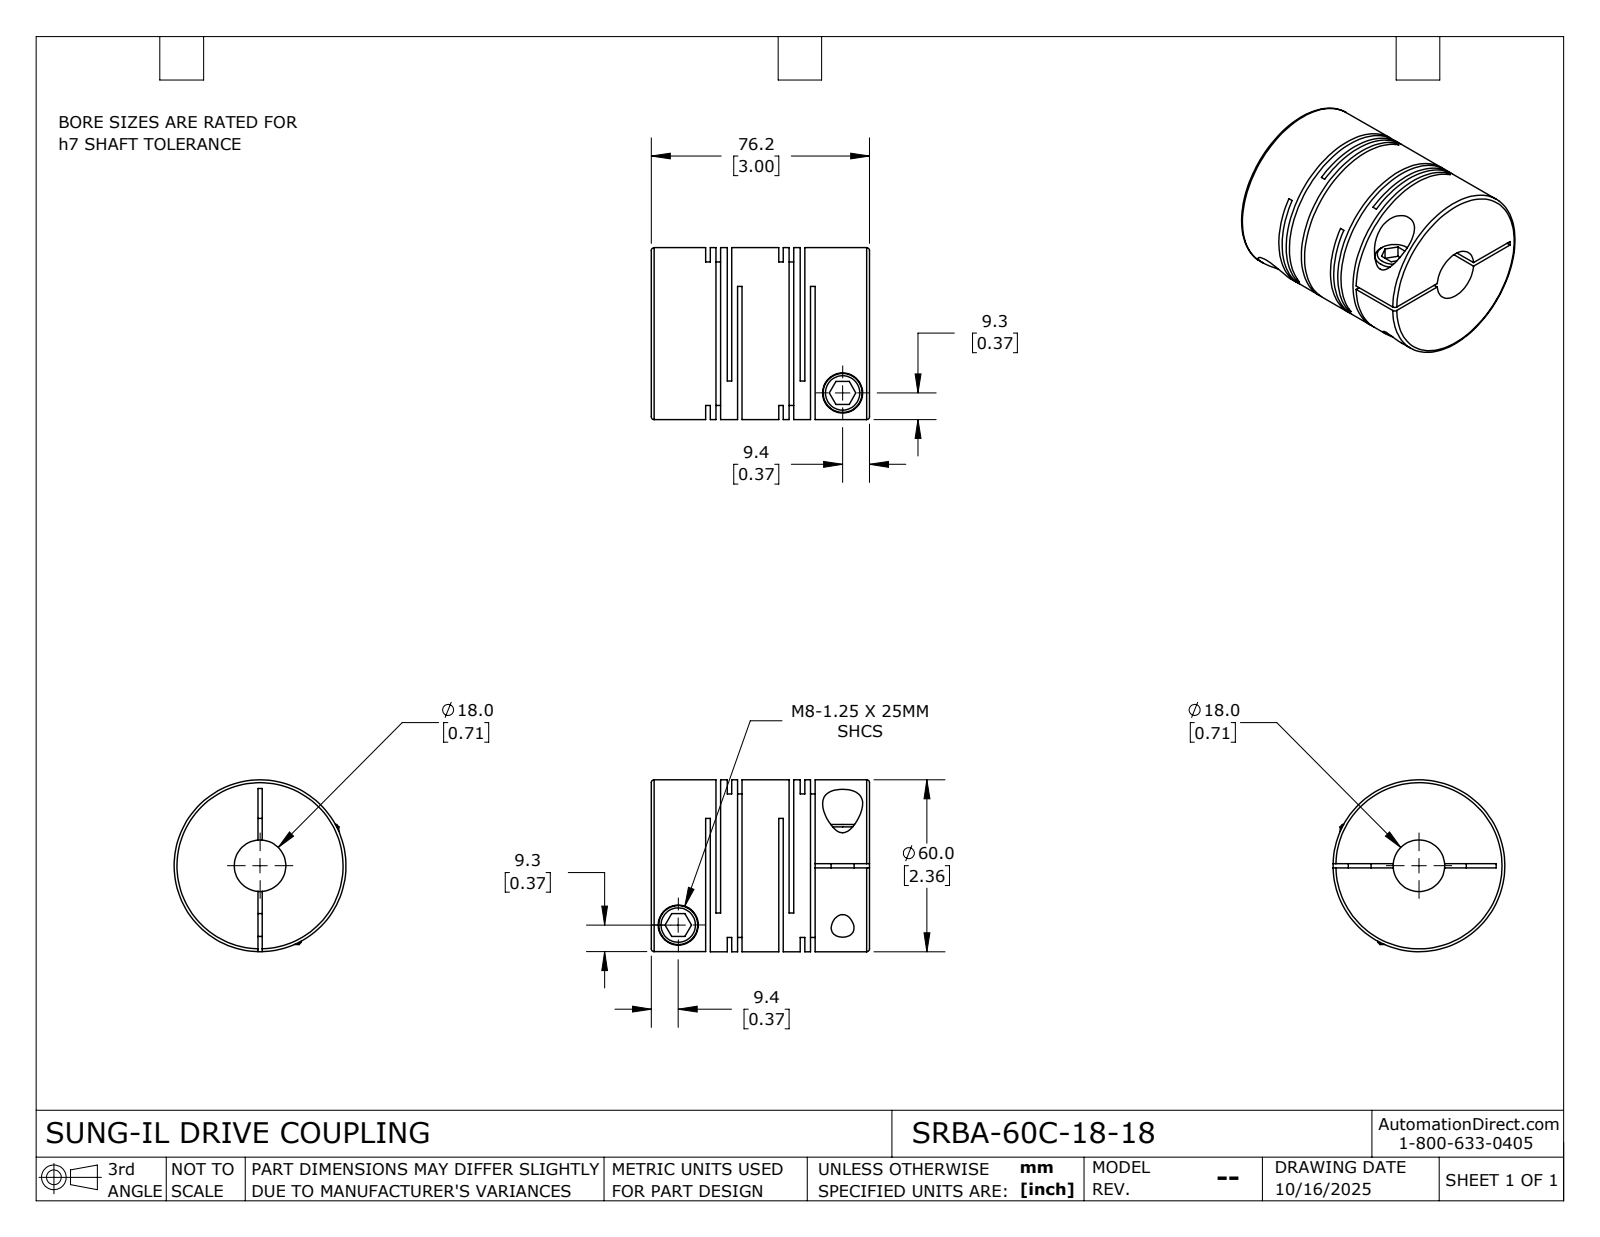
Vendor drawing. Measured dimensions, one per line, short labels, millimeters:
name: SRBA-60C-18-18
written by: SolidWorks 2024 (CONFIG_CONTROL_DESIGN)
unit: mm
bodies: 1 solid, 115 faces (60 planar, 42 cylindrical, 13 other)
size: 76.2 × 60 × 60
volume: 163 948 mm³; area: 59 938 mm²
holes: 2× ⌀8, 2× ⌀14, 1× ⌀18
bosses: 2× ⌀13.6, 1× ⌀60
face distances: 1.6, 25.5, 3.6, 7.5, 33, 2, 5.9, 23.9, 3.9, 21.9
